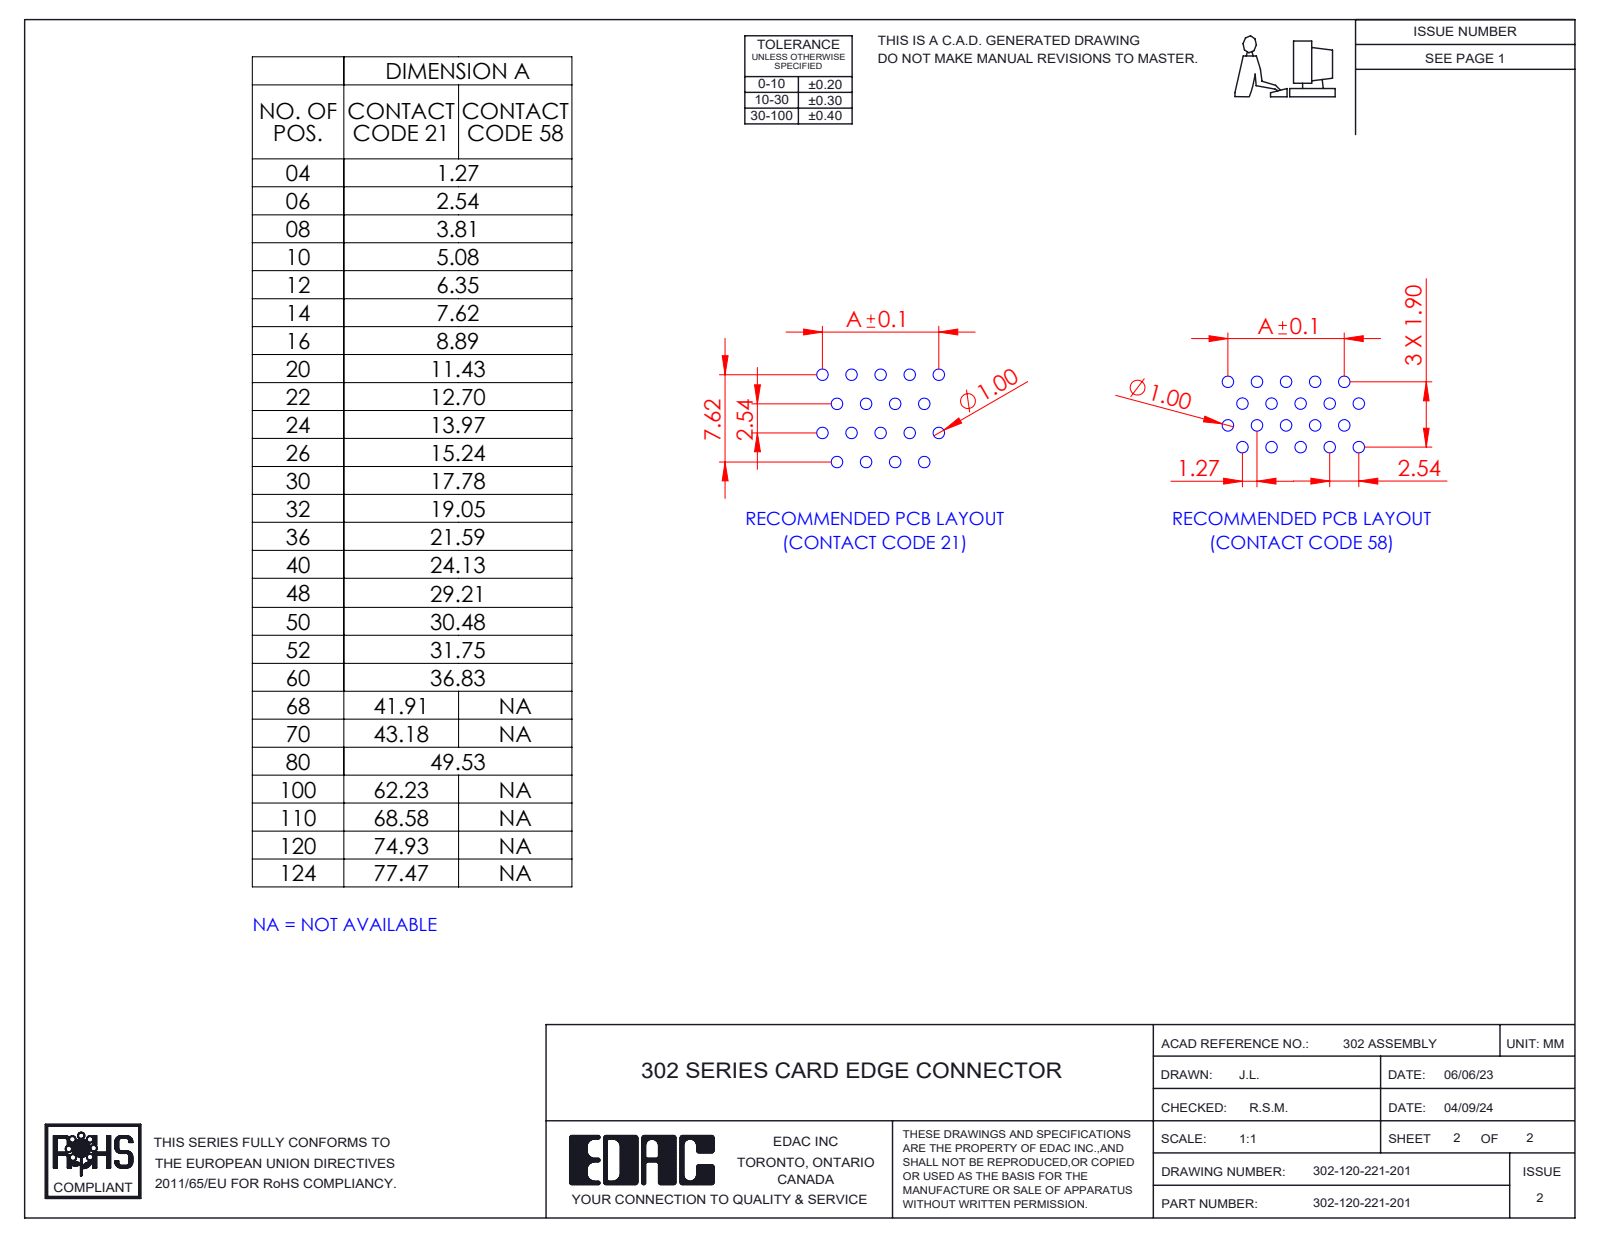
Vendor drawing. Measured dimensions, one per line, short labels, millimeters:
name: 302-120-221-201; Contact_302-290-X21 (1); Contact_302-290-X21 (2); HSG_Vertical HSG
written by: SolidWorks 2023 (CONFIG_CONTROL_DESIGN)
unit: mm
bodies: 121 solids, 5526 faces (4069 planar, 1213 cylindrical, 244 other)
size: 82.3 × 17.63 × 8.88
volume: 6 254 mm³; area: 17 951 mm²
rounds: 128× R0.2, 4× R2.03, 4× R2.09, 2× R0.11, 2× R0.4, 2× R0.41, 2× R1.25, 2× R1.53
face distances: 8.88, 2.54, 5.08, 3.8, 7.62, 3.49, 5.39, 1.9, 10.16, 6.34
